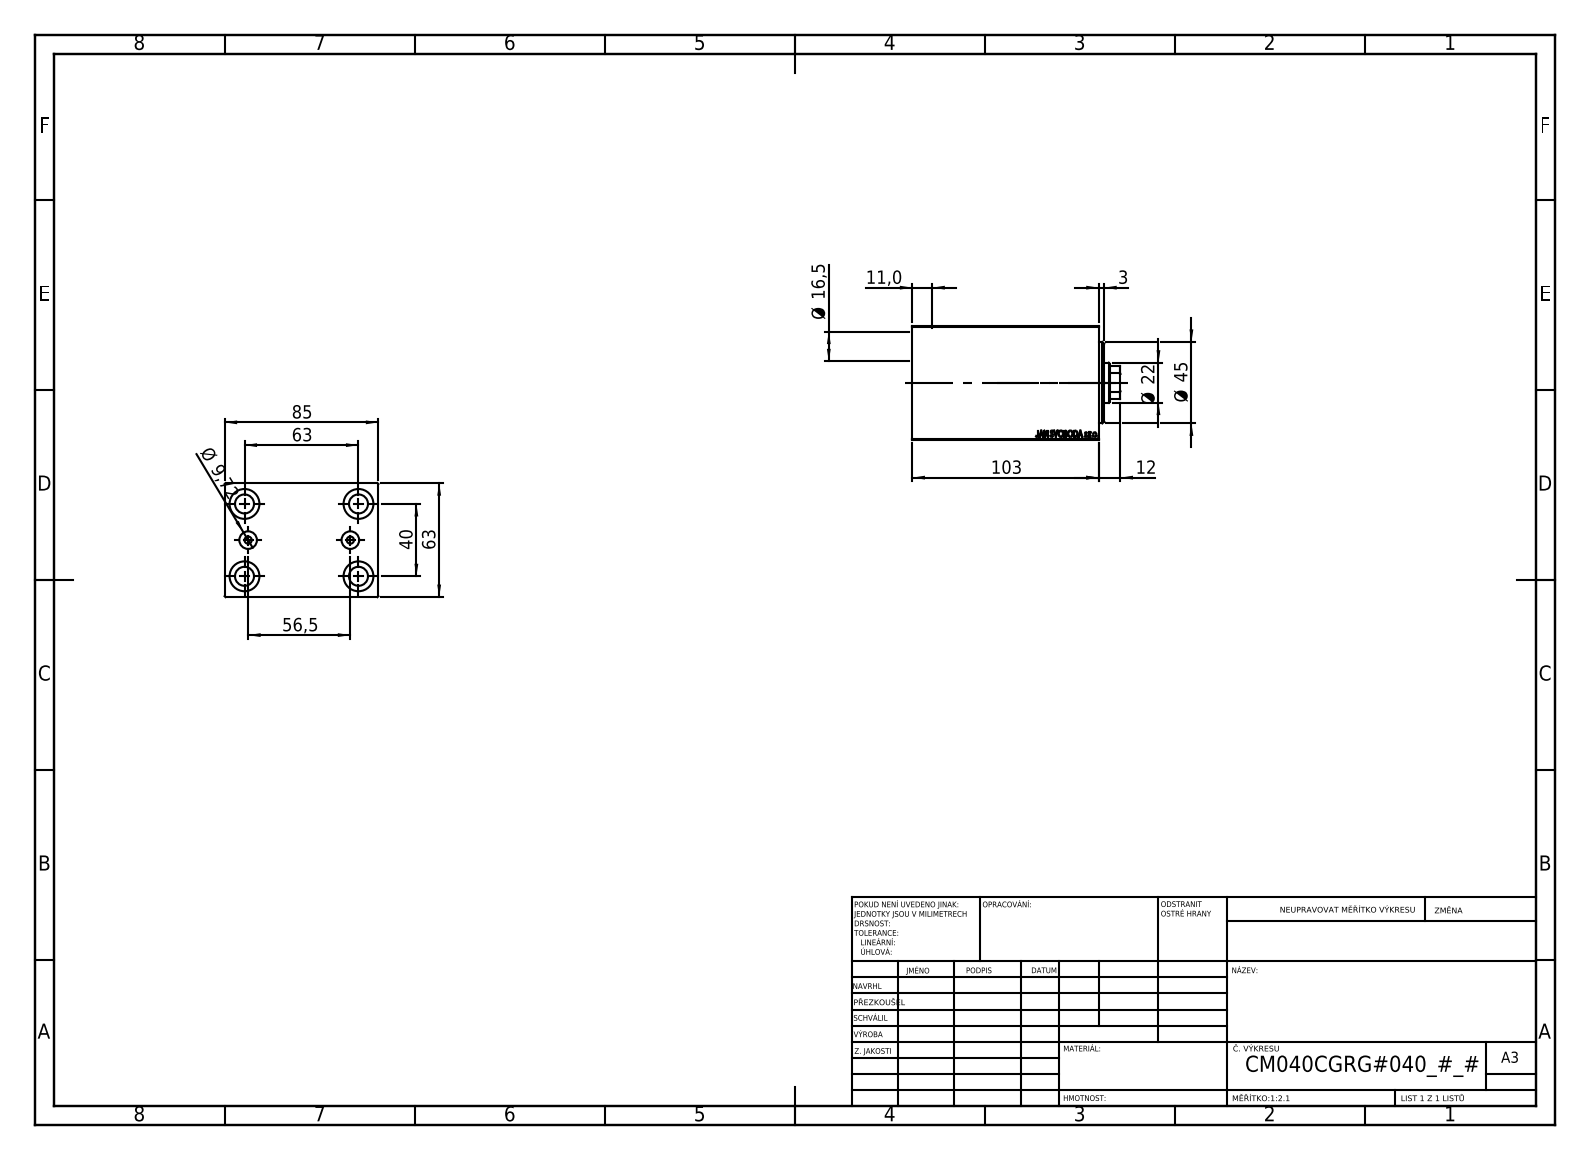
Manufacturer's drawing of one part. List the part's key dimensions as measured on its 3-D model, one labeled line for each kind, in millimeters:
Part name (STEP PRODUCT): V450CM_VC_B; V450CM_C_Body; V450CM_C_VCP
STEP written by: SolidWorks 2019 (CONFIG_CONTROL_DESIGN)
Units: millimetres
Bodies: 3 solids, 858 faces (408 planar, 56 cylindrical, 394 other)
Overall size (bounding box): 115 × 85 × 63
Volume: 470 756 mm³ · Surface area: 88 068 mm²
Round holes (diameter × count): ⌀10.5 ×4, ⌀16.5 ×4, ⌀4 ×2, ⌀9.72 ×2, ⌀12.5 ×1, ⌀22 ×1, ⌀25.5 ×1, ⌀40 ×1, ⌀42 ×1, ⌀45 ×1
Partial cylindrical surfaces — rounded edges, fillets, slot ends (radius × count): R10.5 ×1
Main face-to-face distances: 63, 85, 12, 91, 103, 40, 1, 79, 11, 80
Hole centre spacings: 37.31, 20.1, 20.5, 40, 61.82, 63, 64.2, 74.63
